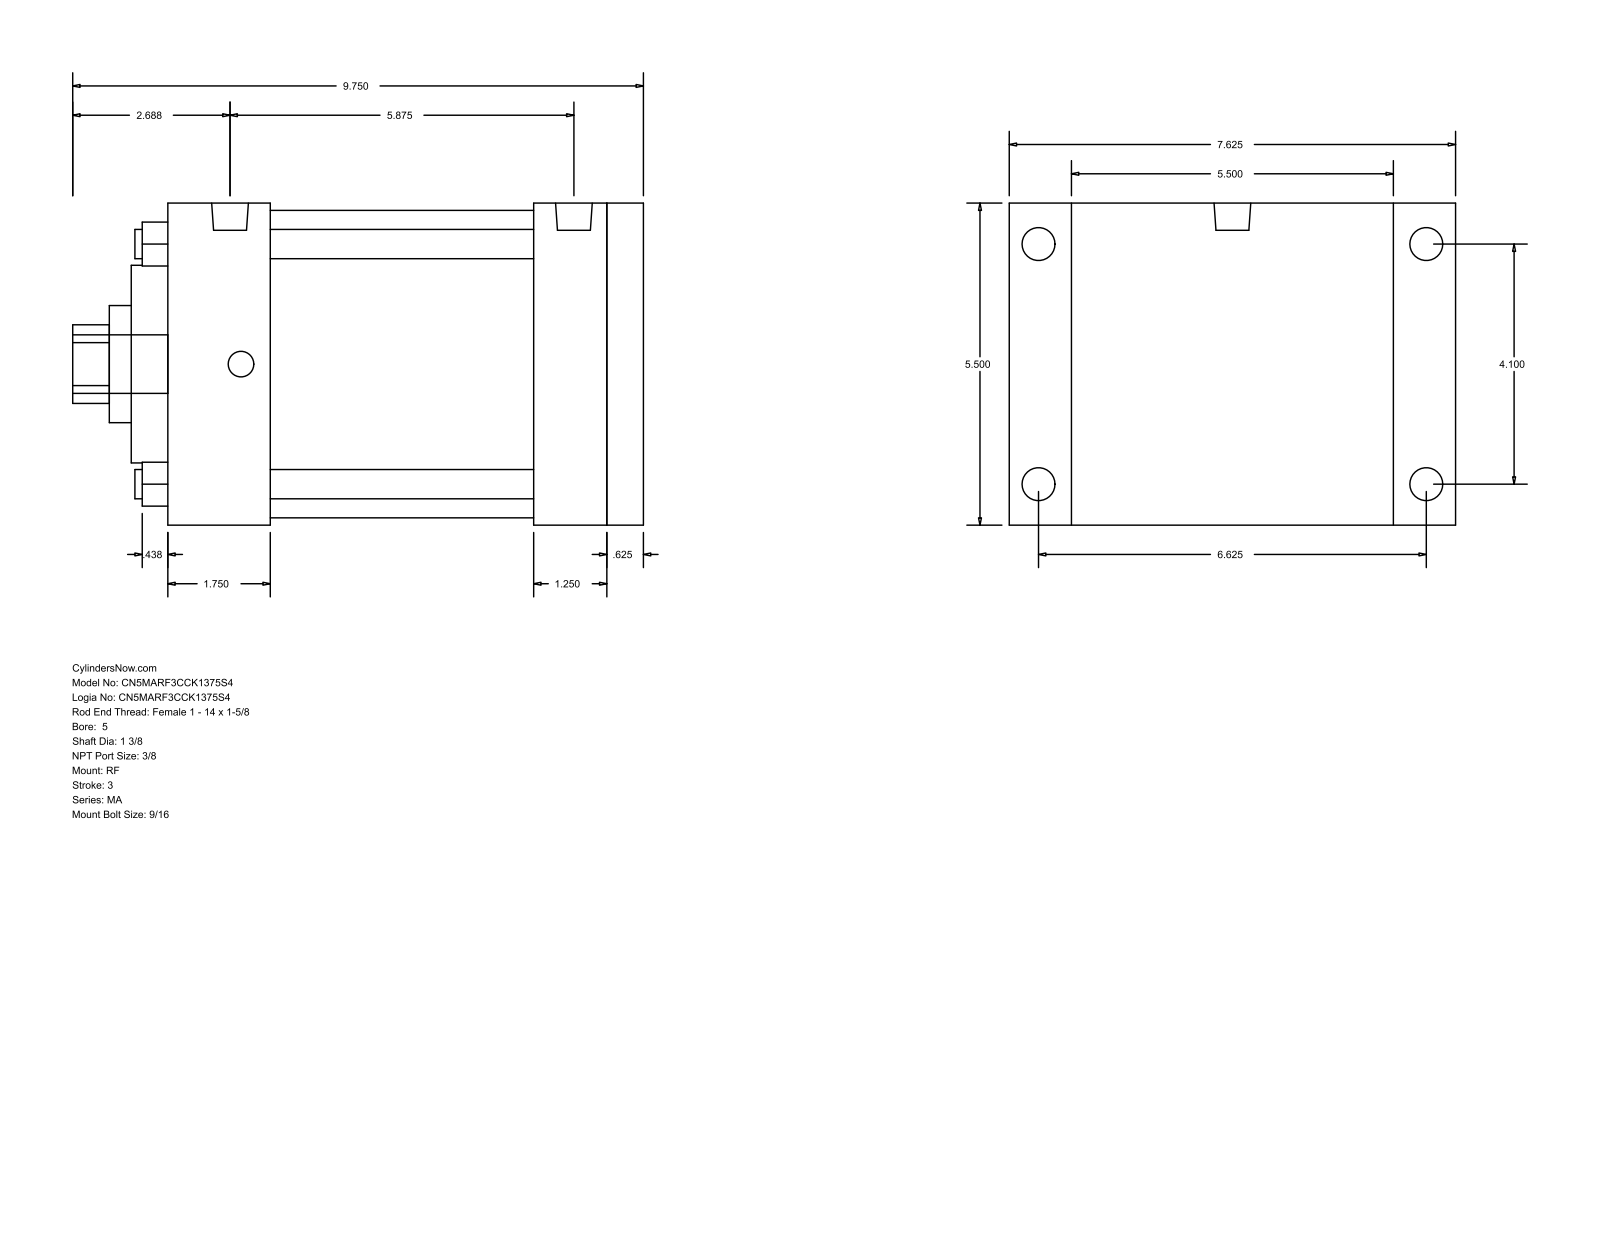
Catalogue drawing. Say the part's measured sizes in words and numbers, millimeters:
The part is named "MA_RF__0500_1.375". Its 3-D file was written by "GSSL Pune (CONFIG_CONTROL_DESIGN)". It is 0 solids with 94 faces: 65 planar, 29 cylindrical and 0 other. Overall it measures 247.65 by 193.68 by 139.7 millimeters. Round holes: 4 of diameter 12.7, 1 of diameter 34.92, 1 of diameter 50.8, 1 of diameter 85.72, 1 of diameter 133.35. Round bosses or shafts: 4 of diameter 14.29, 4 of diameter 11.11, 2 of diameter 15.93, 1 of diameter 25.4. Partial cylindrical surfaces (rounded edges, fillets, slot ends): 1 of radius 17.06. The main face-to-face distances are 139.7, 206.38, 15.87, 190.51, 44.45, 146.06, 161.93, 158.76, 114.31, 31.75. The hole center spacings are 73.64, 104.14, 147.28.
